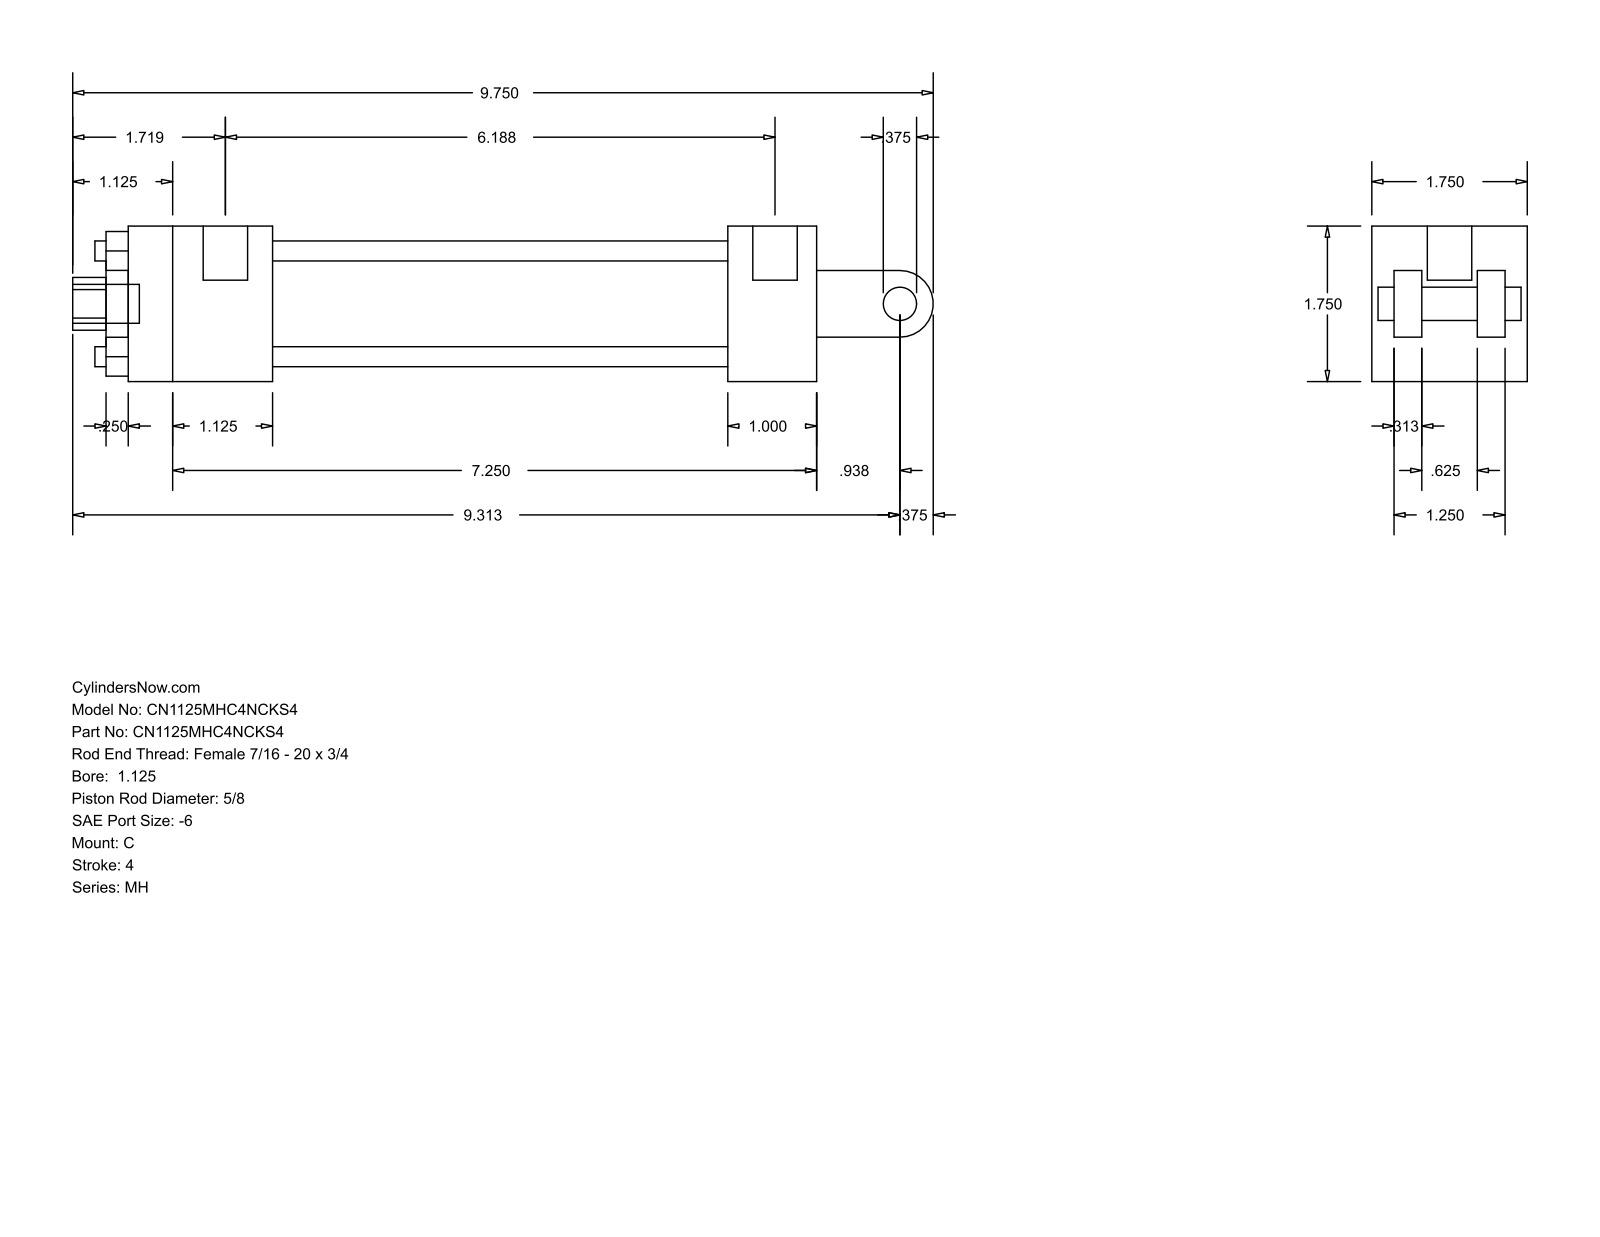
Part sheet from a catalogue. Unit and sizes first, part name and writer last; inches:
Units: inches
Overall size (bounding box): 9.687 × 1.75 × 1.75
Round holes (diameter × count): ⌀0.225 ×4, ⌀0.219 ×2, ⌀0.5 ×1, ⌀0.625 ×1, ⌀1.125 ×1, ⌀1.375 ×1
Round bosses / shafts (diameter × count): ⌀0.219 ×2, ⌀0.5 ×1, ⌀0.437 ×1, ⌀0.375 ×1
Partial cylindrical surfaces — rounded edges, fillets, slot ends (radius × count): R0.297 ×1, R0.375 ×1
Main face-to-face distances: 1.75, 0.25, 1.25, 0.563, 0.5, 1.188, 1.5, 0.313, 0.938, 1
Hole centre spacings: 0.841, 1.19, 1.683
Bodies: 0 solids, 99 faces (70 planar, 29 cylindrical, 0 other)
Part name (STEP PRODUCT): MH_C__0112_0.625
STEP written by: GSSL Pune (CONFIG_CONTROL_DESIGN)
